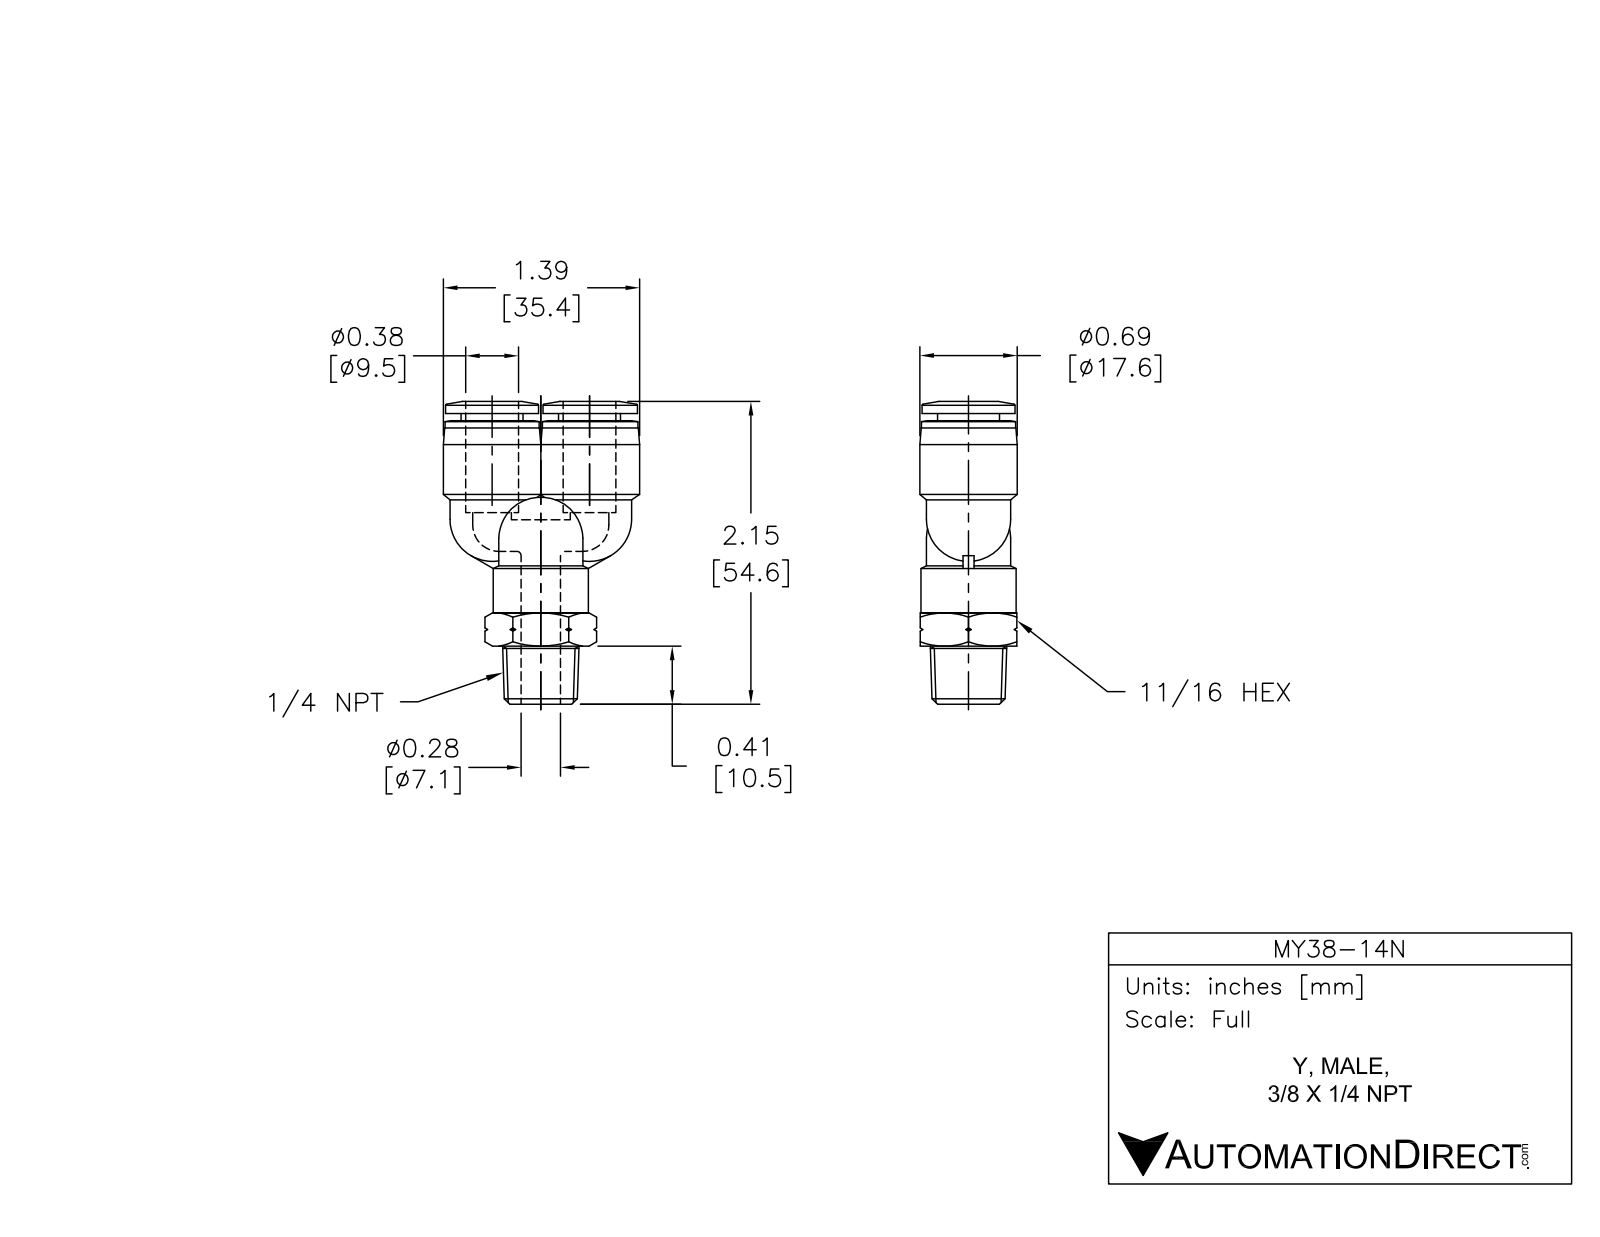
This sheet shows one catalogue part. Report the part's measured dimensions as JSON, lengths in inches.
{"part_name": "MY38-14N", "step_written_by": "SolidWorks 2015 (AUTOMOTIVE_DESIGN)", "units": "inches", "bodies": {"solids": 1, "faces": 122, "planar": 22, "cylindrical": 32, "other": 68}, "overall_size": [2.154, 1.386, 0.693], "volume_in3": 0.764, "surface_area_in2": 11.55, "round_holes": [[0.386, 2], [0.276, 1]], "round_bosses_or_shafts": [[0.598, 3], [0.693, 2], [0.669, 2], [0.661, 2], [0.441, 2], [0.677, 1]], "face_to_face_distances": [0.687, 0.051, 1.602, 1.654, 0.709, 0.945, 0.657, 0.413, 1.358, 2.016], "hole_center_spacings": [0.346, 0.693]}
